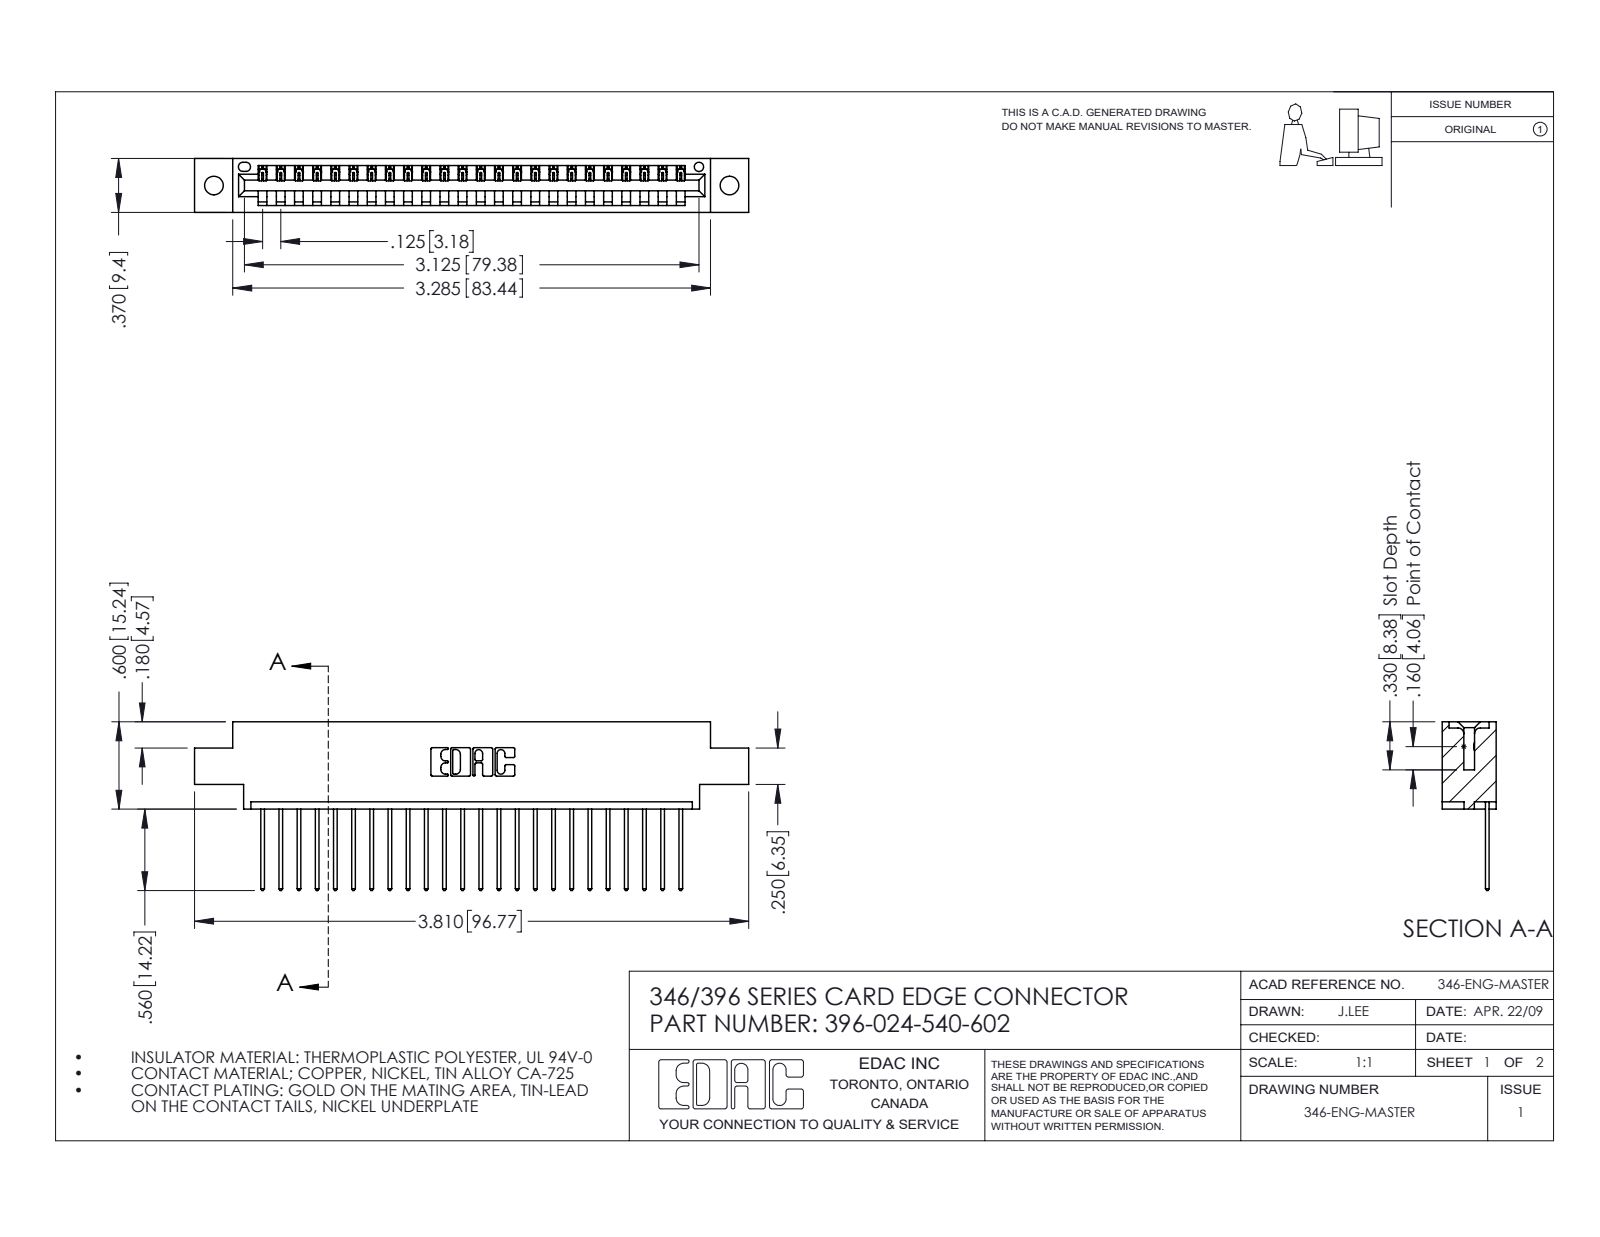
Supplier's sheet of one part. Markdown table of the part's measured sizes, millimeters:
| quantity | value |
| --- | --- |
| part name | 346 Part_0.170 Offset - 0.128 Dia; 396-024-540-602; 345-292-001_345-293-140 |
| STEP written by | SolidWorks 2016 (CONFIG_CONTROL_DESIGN) |
| units | millimeters |
| bodies | 25 solids, 1518 faces (1040 planar, 478 cylindrical, 0 other) |
| overall size | 96.8 × 29.5 × 9.4 |
| volume | 8 980 mm³ |
| surface area | 11 150 mm² |
| round holes (diameter × count) | 3.3 × 2, 1.6 × 1 |
| partial cylindrical surfaces (radius × count) | 0.2 × 48, 0.3 × 48, 0.3 × 22, 0.2 × 6, 0.8 × 6, 0.7 × 3, 0.8 × 2, 1 × 2 |
| main face-to-face distances | 1.2, 8.2, 9.4, 6.4, 1.8, 7.6, 0.6, 3.8, 5.6, 2.5 |
| hole center spacings | 6.2, 84.8, 90 |
